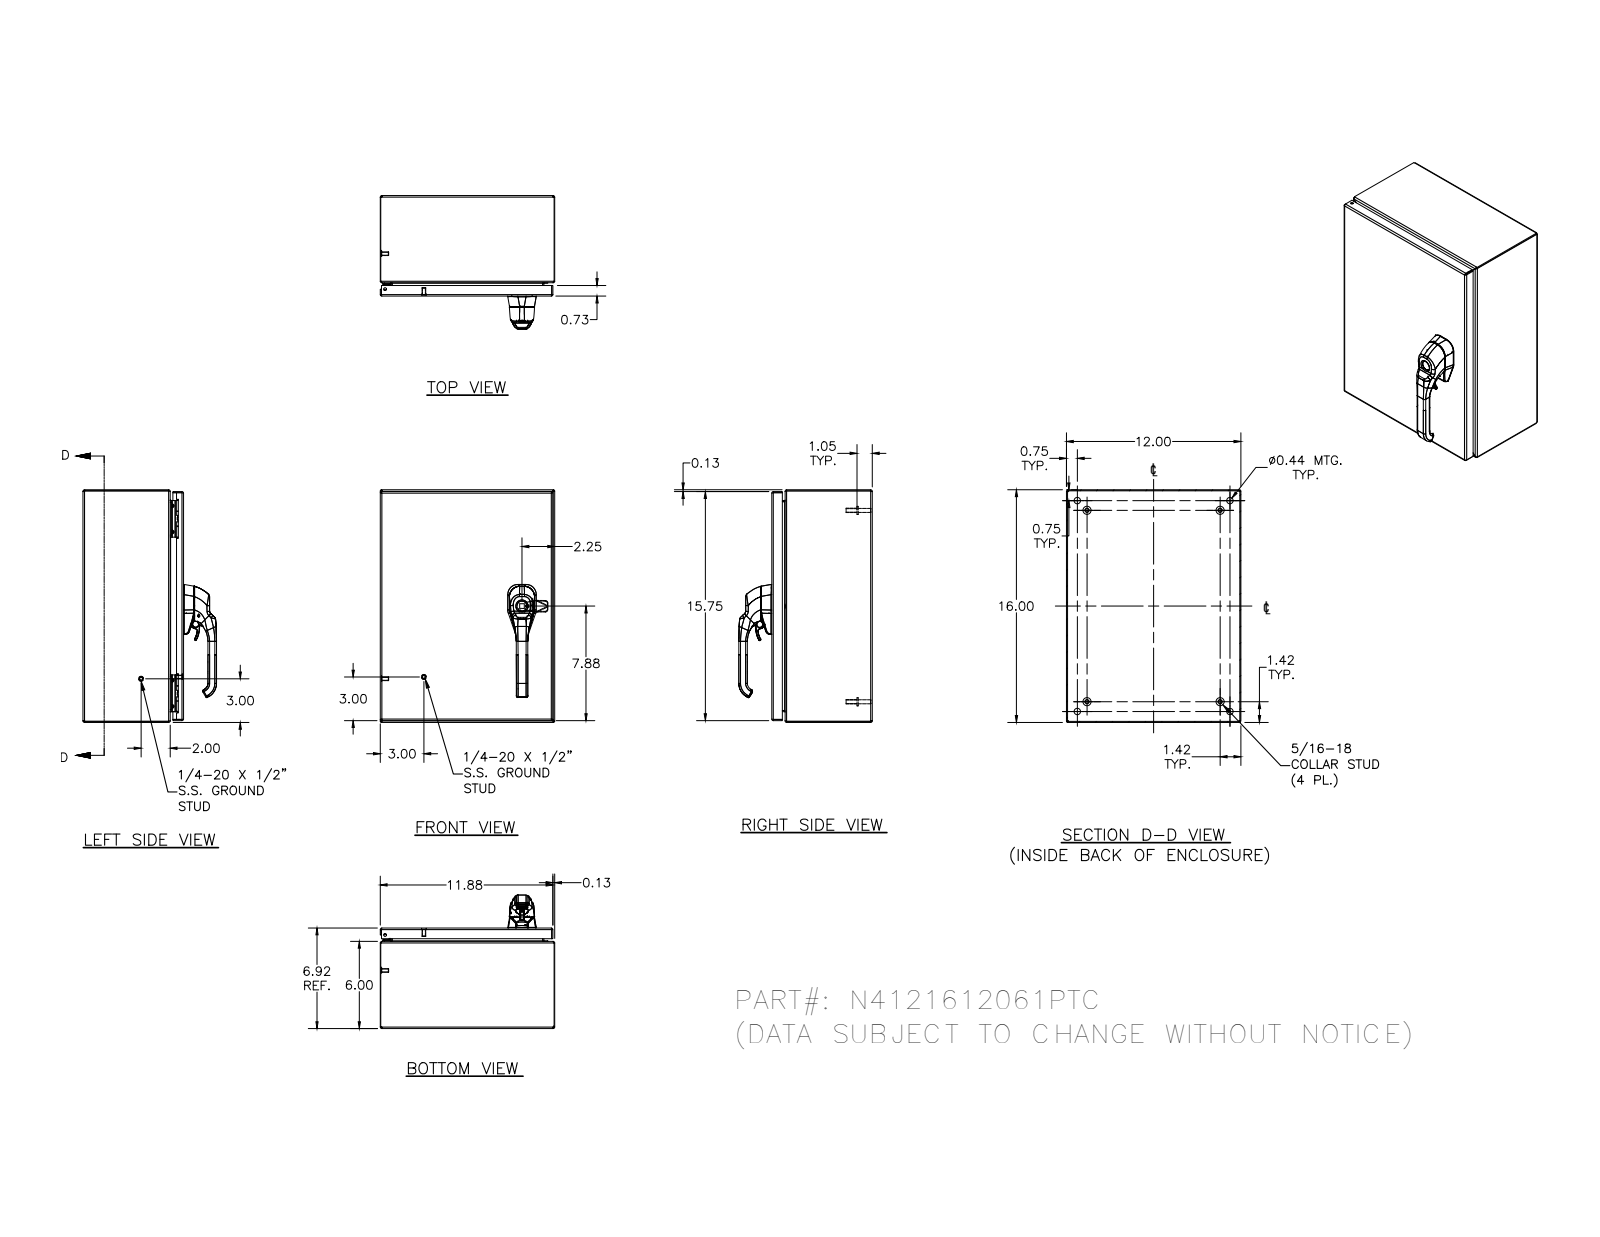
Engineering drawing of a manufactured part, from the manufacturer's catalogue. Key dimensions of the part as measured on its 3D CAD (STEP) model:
Part name (STEP PRODUCT): N4121612061PTC
STEP written by: SolidWorks 2018 (AUTOMOTIVE_DESIGN)
Units: inches
Bodies: 28 solids, 1280 faces (417 planar, 474 cylindrical, 389 other)
Overall size (bounding box): 16 × 12 × 9.095
Volume: 71.64 in³ · Surface area: 1 727 in²
Round holes (diameter × count): ⌀0.188 ×5, ⌀0.093 ×4, ⌀0.152 ×4, ⌀0.167 ×4, ⌀0.172 ×4, ⌀0.437 ×4, ⌀0.28 ×3, ⌀0.156 ×2, ⌀0.187 ×1
Round bosses / shafts (diameter × count): ⌀0.25 ×10, ⌀0.563 ×4, ⌀0.36 ×4, ⌀0.32 ×4, ⌀0.3 ×4, ⌀0.275 ×4, ⌀0.256 ×4, ⌀0.164 ×4
Partial cylindrical surfaces — rounded edges, fillets, slot ends (radius × count): R0.031 ×30, R0.05 ×26, R0.105 ×20, R0.016 ×18, R0.125 ×14, R0.032 ×8, R0.067 ×8, R0.068 ×8
Main face-to-face distances: 0.074, 6.843, 6.917, 11.926, 6.769, 15.926, 12, 11.852, 16, 15.852
Hole centre spacings: 11.996, 0.017, 0.66, 12.656, 0.019, 0.5, 0.648, 0.656
